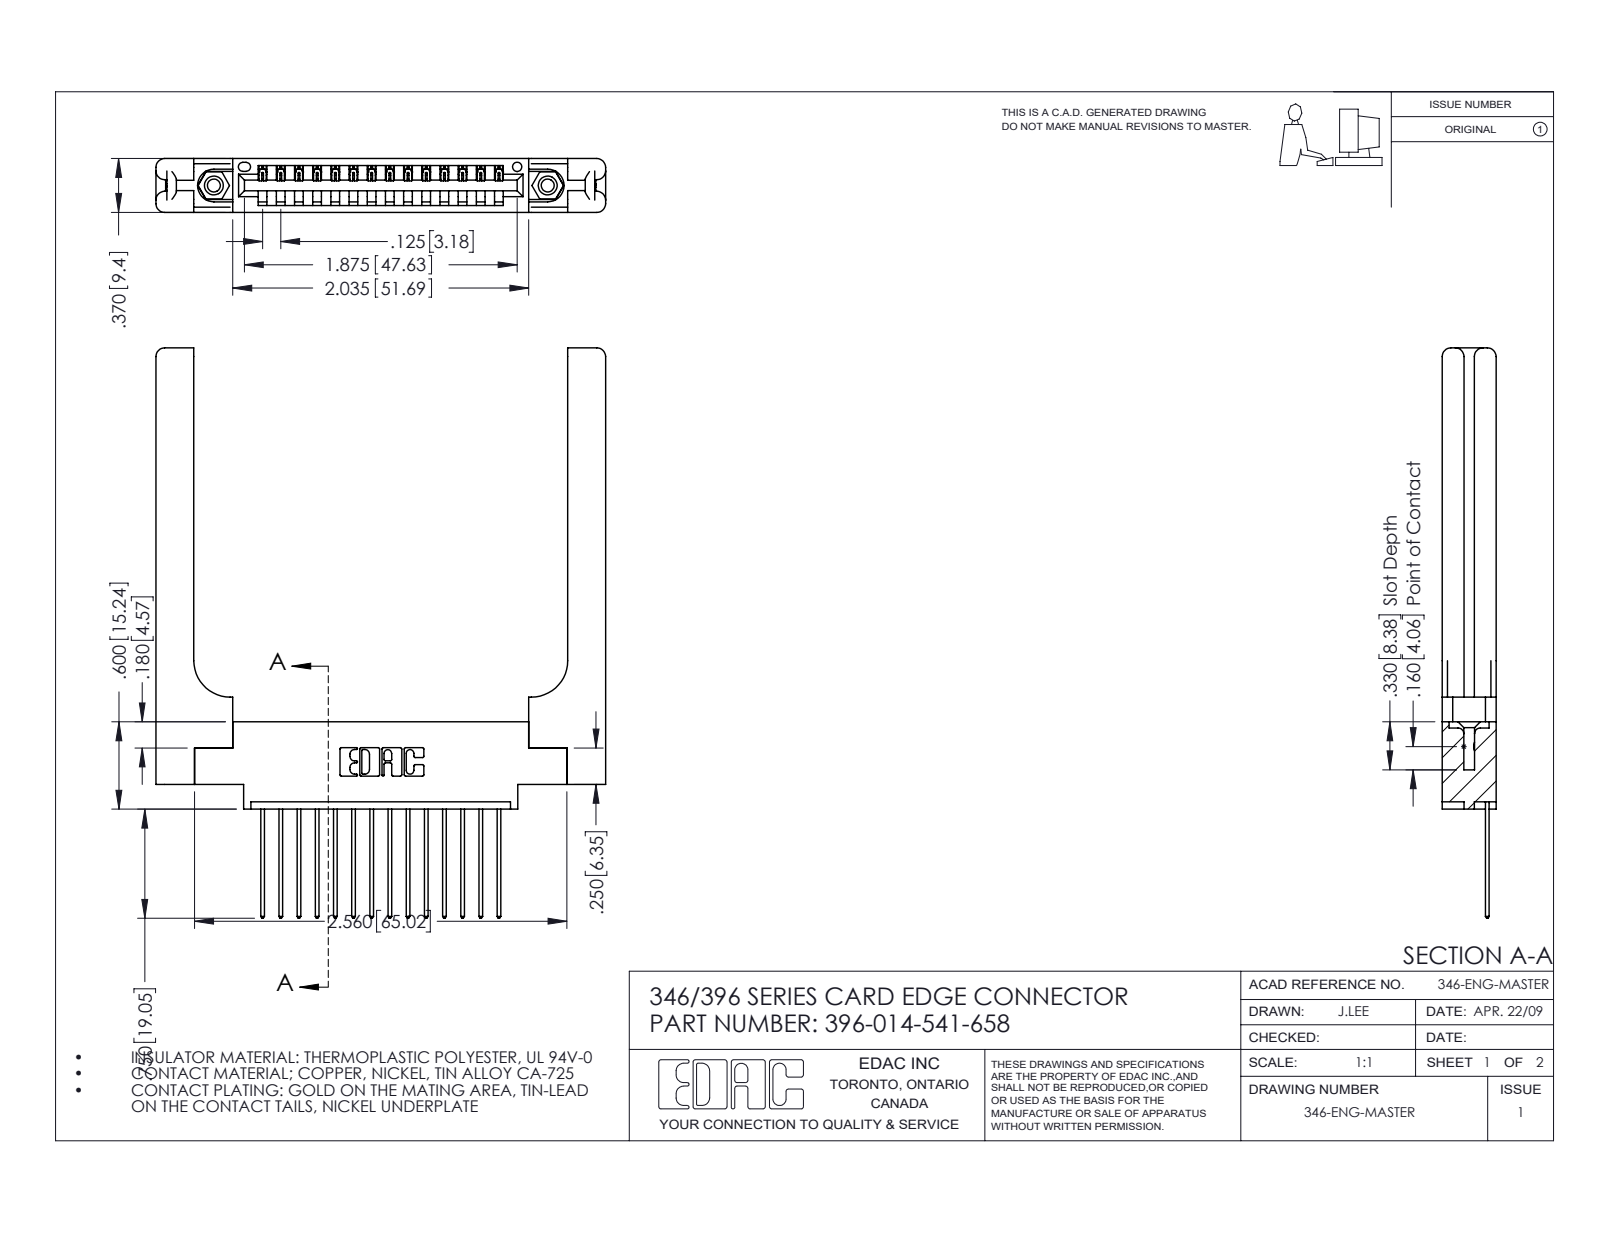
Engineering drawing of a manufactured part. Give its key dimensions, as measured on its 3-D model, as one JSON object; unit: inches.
{"part_name": "346 Part_0.170 Offset - 0.156 Dia-TH; 396-014-541-658; 346-220-058_345-220-058; 345-250-001_345-250-001-102 (+1 more)", "step_written_by": "SolidWorks 2016 (CONFIG_CONTROL_DESIGN)", "units": "inches", "bodies": {"solids": 19, "faces": 1194, "planar": 788, "cylindrical": 346, "other": 60}, "overall_size": [3.92, 3.091, 0.37], "volume_in3": 0.899, "surface_area_in2": 22.2, "round_holes": [[0.089, 2], [0.125, 2], [0.156, 2], [0.064, 1]], "round_bosses_or_shafts": [[0.155, 2]], "partial_cylinders_radius": [[0.006, 28], [0.01, 28], [0.01, 22], [0.06, 16], [0.007, 6], [0.031, 6], [0.026, 3], [0.03, 2]], "face_to_face_distances": [0.37, 0.15, 0.072, 0.148, 0.048, 0.322, 0.22, 0.25, 0.102, 0.173], "hole_center_spacings": [0.246, 2.089, 2.295]}
